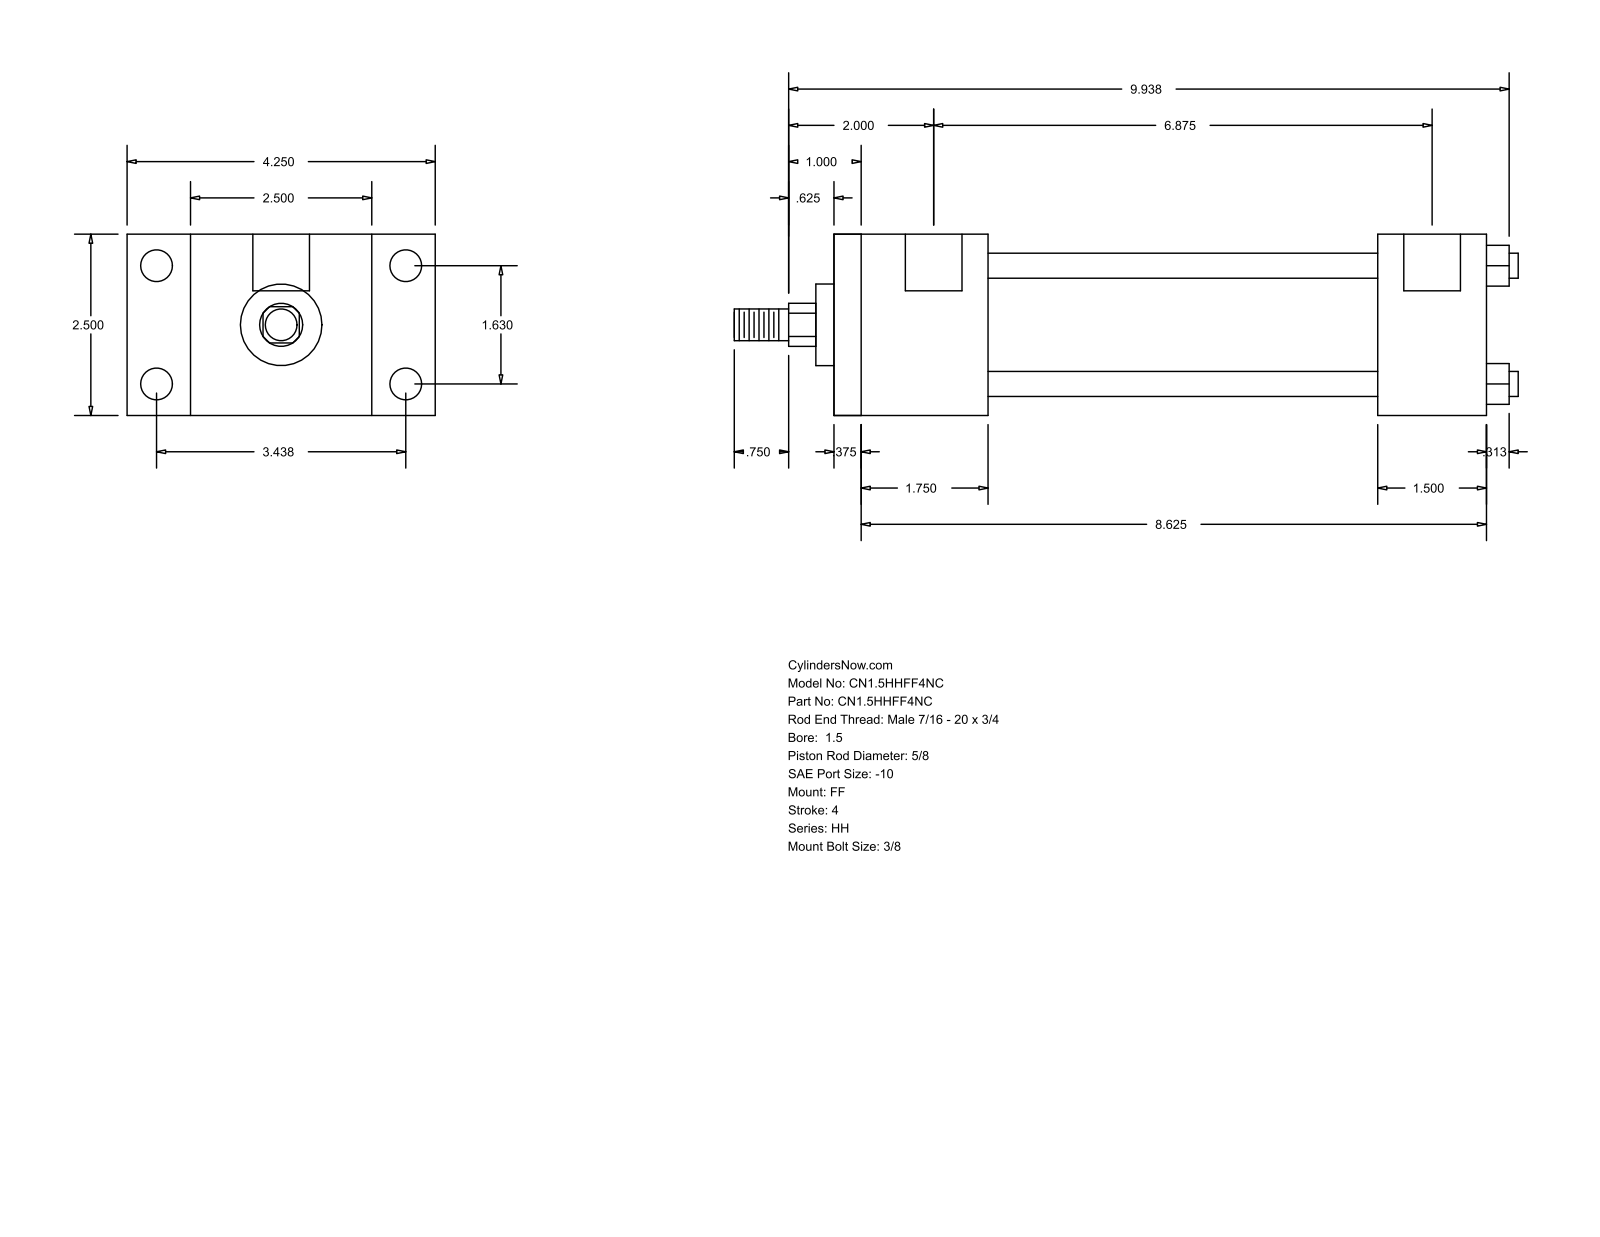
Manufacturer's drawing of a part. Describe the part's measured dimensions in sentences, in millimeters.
The part is named "HH_FF__0150_0.625". Its 3-D file was written by "GSSL Pune (CONFIG_CONTROL_DESIGN)". It is 0 solids with 92 faces: 64 planar, 28 cylindrical and 0 other. Overall it measures 274.64 by 107.95 by 63.5 millimeters. Round holes: 4 of diameter 5.56, 4 of diameter 11.13, 2 of diameter 19.84. Round bosses or shafts: 4 of diameter 8.76, 1 of diameter 44.45, 1 of diameter 28.57, 1 of diameter 15.88, 1 of diameter 11.11. Partial cylindrical surfaces (rounded edges, fillets, slot ends): 1 of radius 7.54. The main face-to-face distances are 63.5, 228.59, 9.52, 219.07, 44.45, 53.97, 174.62, 190.5, 180.98, 136.53. The hole center spacings are 41.4, 87.32, 96.64, 177.8, 1.58, 1.59, 174.63, 176.21.
